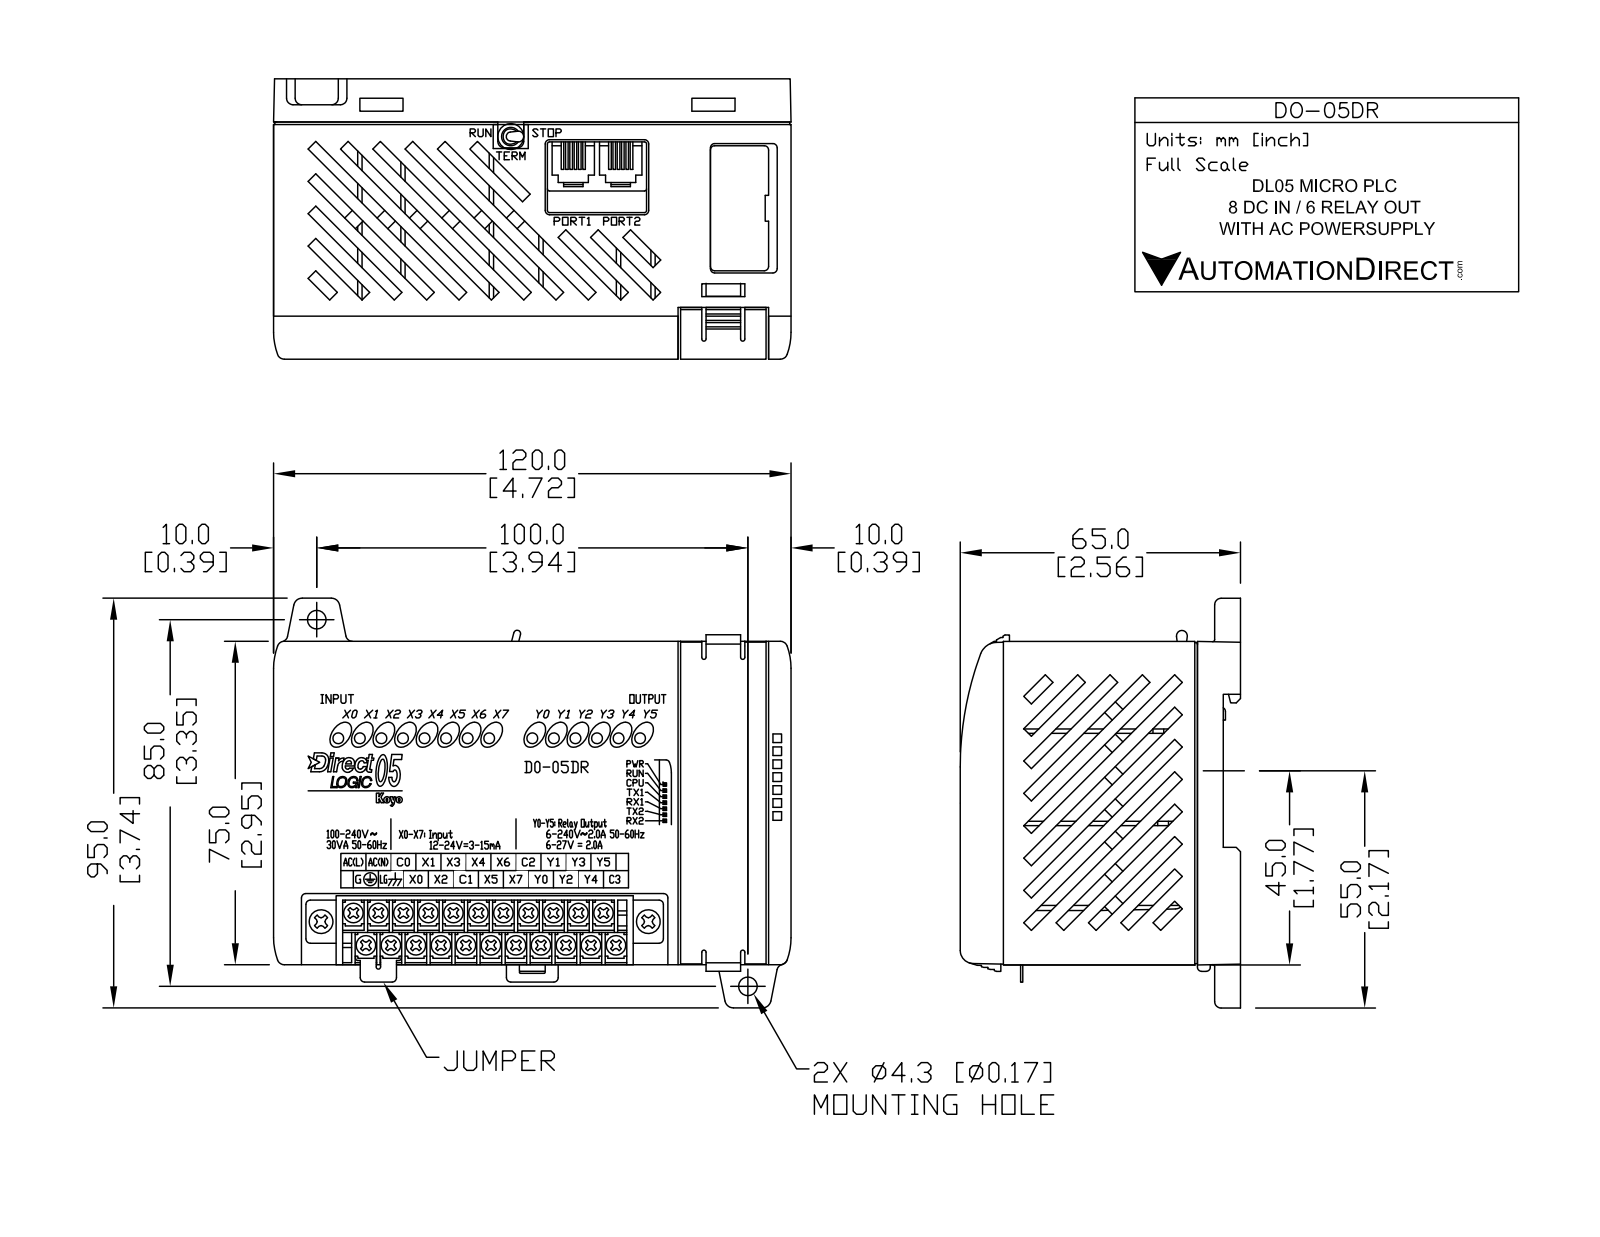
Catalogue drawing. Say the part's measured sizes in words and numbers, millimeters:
The part is named "D0-05DR". Its 3-D file was written by "SolidWorks 2009 (AUTOMOTIVE_DESIGN)". It is 3 solids with 989 faces: 676 planar, 95 cylindrical and 218 other. Overall it measures 120 by 95 by 65.06 millimeters. Its volume is 65 415 cubic millimeters and its surface area 91 009 square millimeters. Round holes: 2 of diameter 4.3. Round bosses or shafts: 22 of diameter 4.42, 2 of diameter 4.5. Partial cylindrical surfaces (rounded edges, fillets, slot ends): 4 of radius 1, 4 of radius 2, 2 of radius 1.5, 1 of radius 63.5, 1 of radius 65. The main face-to-face distances are 1.5, 73.5, 59.5, 4, 63.5, 118.5, 75, 72, 5.5, 65. The hole center spacings are 131.24.
